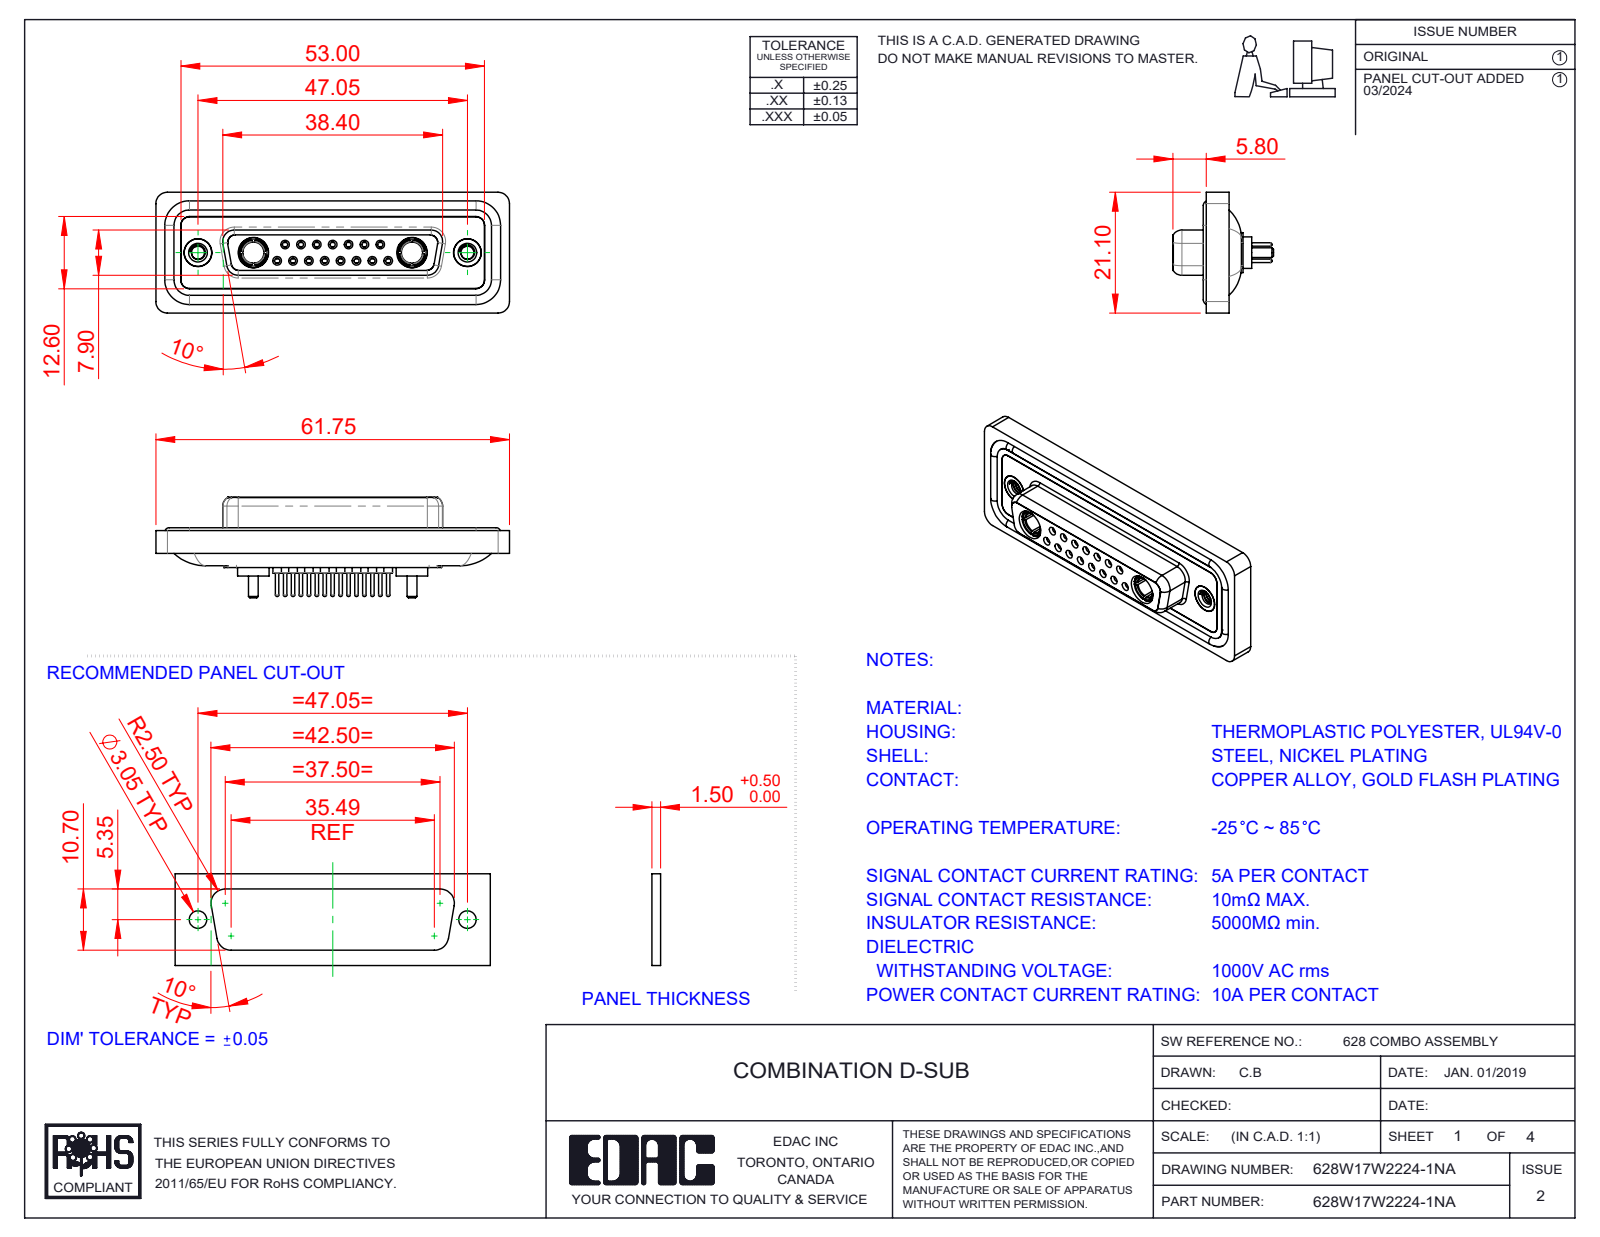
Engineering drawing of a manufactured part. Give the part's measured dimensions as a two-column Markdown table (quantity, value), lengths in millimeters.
| quantity | value |
| --- | --- |
| part name | 628Combo Waterproof Housing_25 Contacts; 628Combo Shell Front_25 Contacts; Power Socket_10A S; 628Combo Contact Row 1_24 (+5 more) |
| STEP written by | SolidWorks 2023 (CONFIG_CONTROL_DESIGN) |
| units | millimeters |
| bodies | 26 solids, 1357 faces (388 planar, 521 cylindrical, 448 other) |
| overall size | 61.75 × 21.1 × 17.55 |
| volume | 8 296 mm³ |
| surface area | 13 828 mm² |
| round holes (diameter × count) | 0.9 × 15, 1.1 × 15, 1.5 × 15, 2 × 15, 1.6 × 8, 1.7 × 7, 4.85 × 4, 2.26 × 2, 3.7 × 2, 4 × 2, 4.05 × 2, 5 × 2 |
| round bosses / shafts (diameter × count) | 2.2 × 15, 0.6 × 15, 1.6 × 11, 5.5 × 2, 5.2 × 2, 4.96 × 2, 4.95 × 2, 4.8 × 2 |
| partial cylindrical surfaces (radius × count) | 1.5 × 22, 2 × 18, 1.35 × 8, 1.6 × 8, 0.25 × 4, 0.5 × 4, 0.6 × 4, 0.65 × 4 |
| main face-to-face distances | 0.4, 1.8, 7.45, 5.65, 6.6, 0.5, 7.05, 1.6, 2.9, 1.1 |
| hole center spacings | 3.16, 2.77, 8.31, 5.54, 5.03, 5.04, 7.49, 11.08 |
